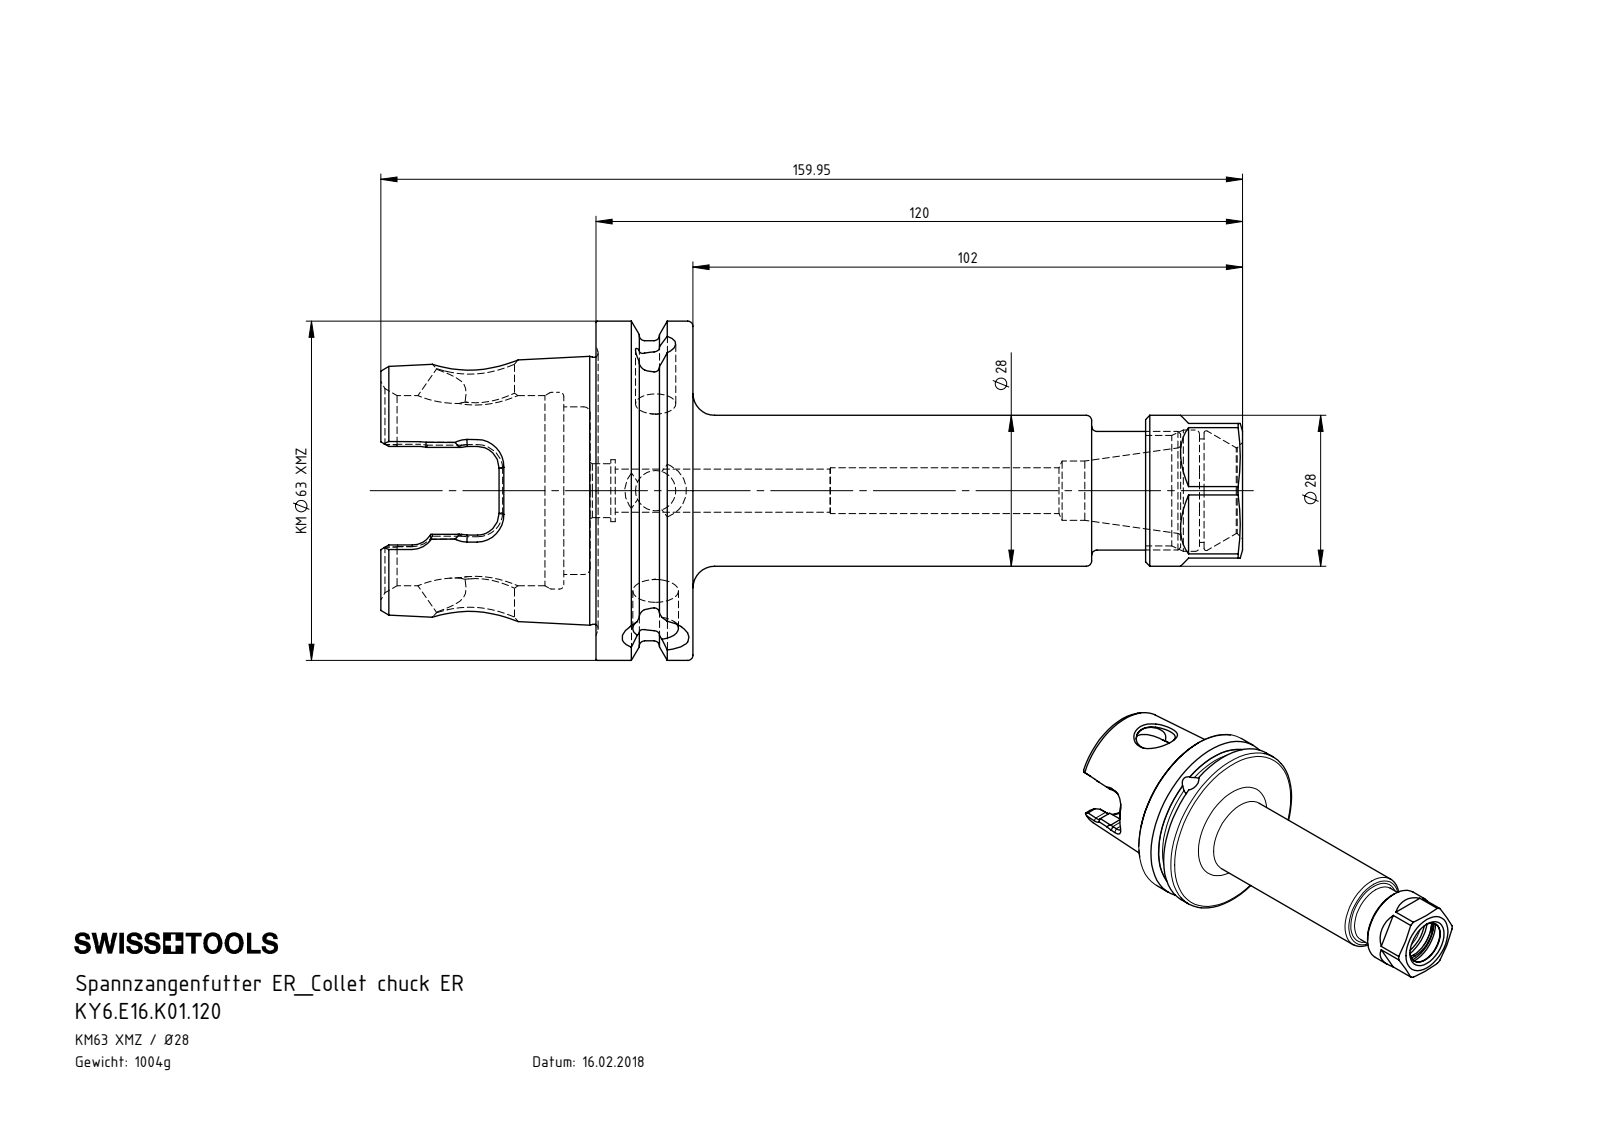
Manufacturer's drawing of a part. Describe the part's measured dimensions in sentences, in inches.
The part is named "KY6.E16.K01.120; ERU-AN4.K01.020_A; E16-ER2.001.018; KY6-E16.K01.120_C". Its 3-D file was written by "SolidWorks 2012 (CONFIG_CONTROL_DESIGN)". It is 3 solids with 317 faces: 100 planar, 72 cylindrical and 145 other. Overall it measures 6.297 by 2.478 by 2.478 inches. Its volume is 7.871 cubic inches and its surface area 53.5 square inches. Round holes: 2 of diameter 0.294, 1 of diameter 0.197, 1 of diameter 0.315, 1 of diameter 0.334, 1 of diameter 0.335, 1 of diameter 0.394, 1 of diameter 0.433, 1 of diameter 0.453, 1 of diameter 0.571, 1 of diameter 0.626, 1 of diameter 0.807, 1 of diameter 0.886. Round bosses or shafts: 1 of diameter 2.478, 1 of diameter 2.193, 1 of diameter 1.102, 1 of diameter 0.866, 1 of diameter 0.354. Partial cylindrical surfaces (rounded edges, fillets, slot ends): 6 of radius 0.157, 2 of radius 0.277, 2 of radius 0.378. The main face-to-face distances are 0.709, 0.043, 0.752, 4.016, 0.984, 4.059, 3.307, 4.724, 0.236, 0.193.
